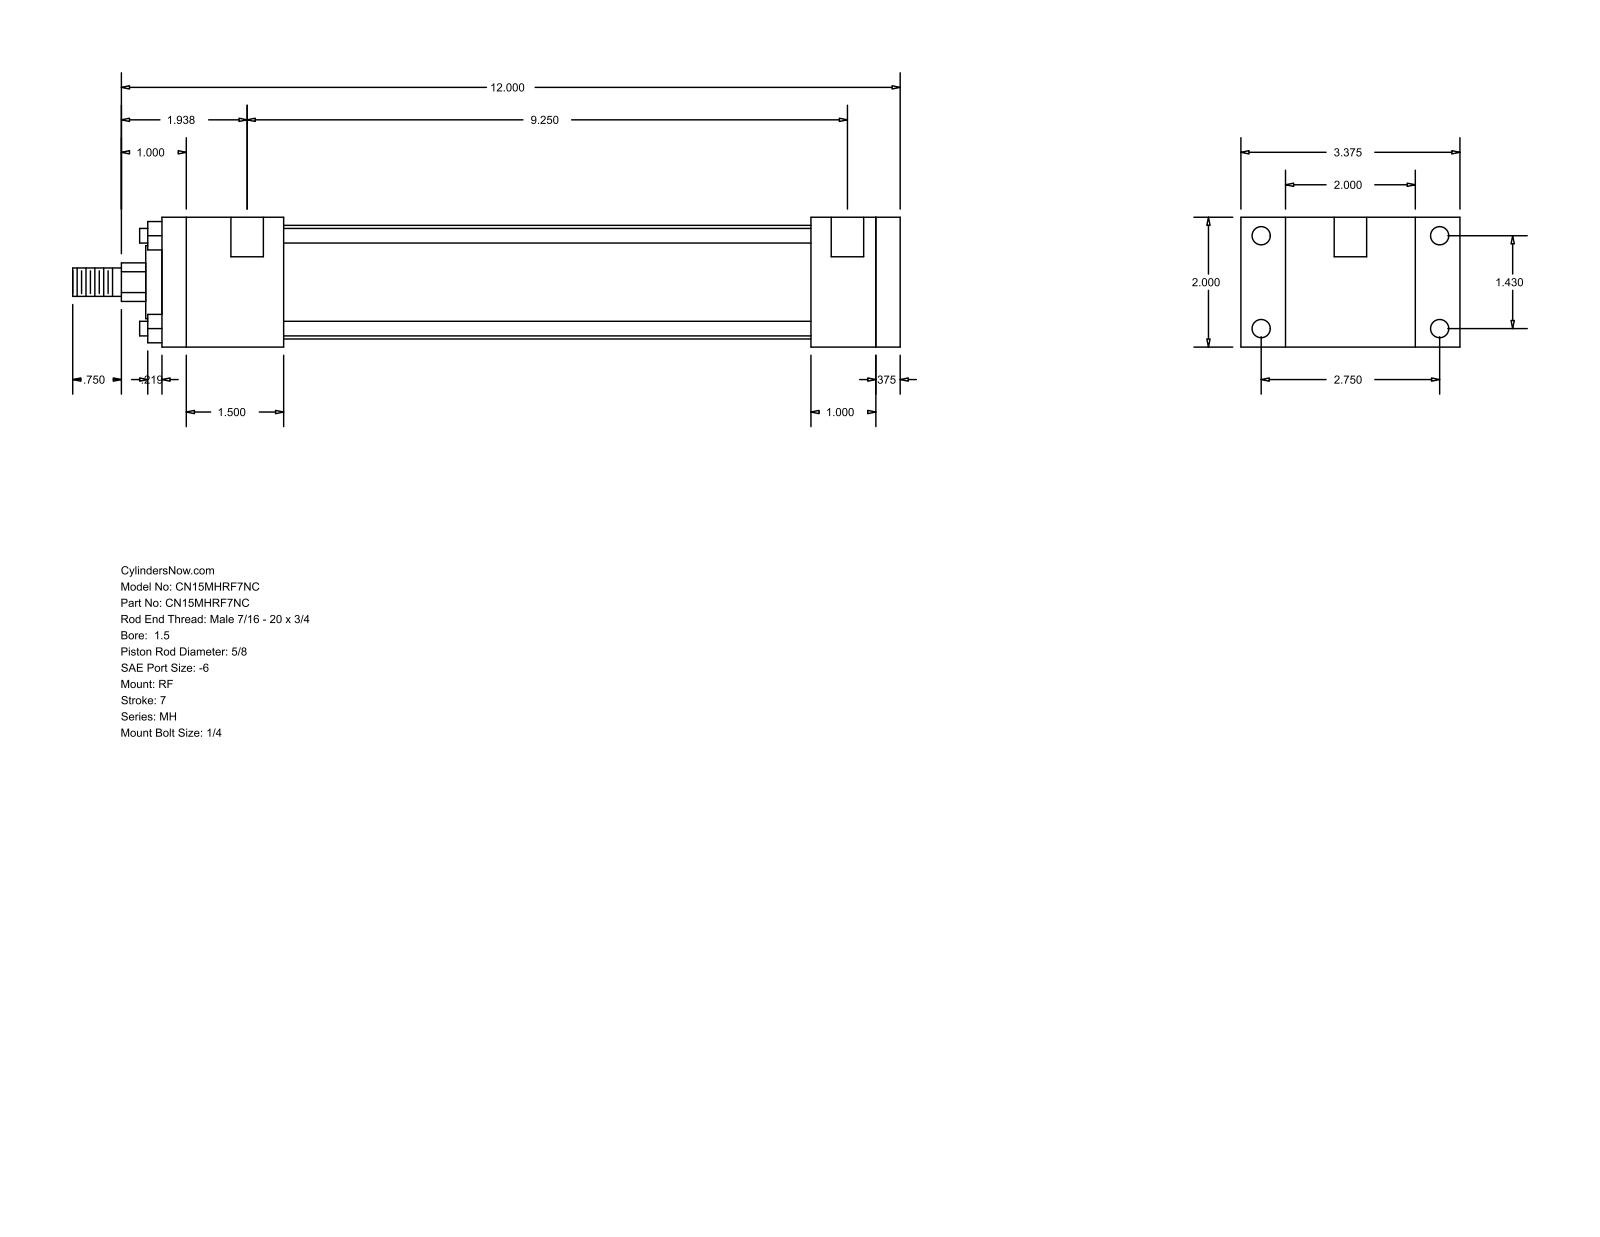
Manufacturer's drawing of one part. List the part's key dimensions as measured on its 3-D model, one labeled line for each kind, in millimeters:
Part name (STEP PRODUCT): MH_RF__0150_0.625
STEP written by: GSSL Pune (CONFIG_CONTROL_DESIGN)
Units: millimetres
Bodies: 0 solids, 92 faces (64 planar, 28 cylindrical, 0 other)
Overall size (bounding box): 323.85 × 85.72 × 50.8
Round holes (diameter × count): ⌀5.56 ×4, ⌀7.14 ×4, ⌀12.7 ×2
Round bosses / shafts (diameter × count): ⌀5.71 ×4, ⌀44.45 ×1, ⌀28.57 ×1, ⌀15.88 ×1, ⌀11.11 ×1
Partial cylindrical surfaces — rounded edges, fillets, slot ends (radius × count): R7.54 ×1
Main face-to-face distances: 50.8, 9.53, 288.92, 279.39, 17.46, 68.26, 254, 25.39, 34.92, 47.62
Hole centre spacings: 36.32, 69.84, 78.72, 238.12, 3.17, 234.95
